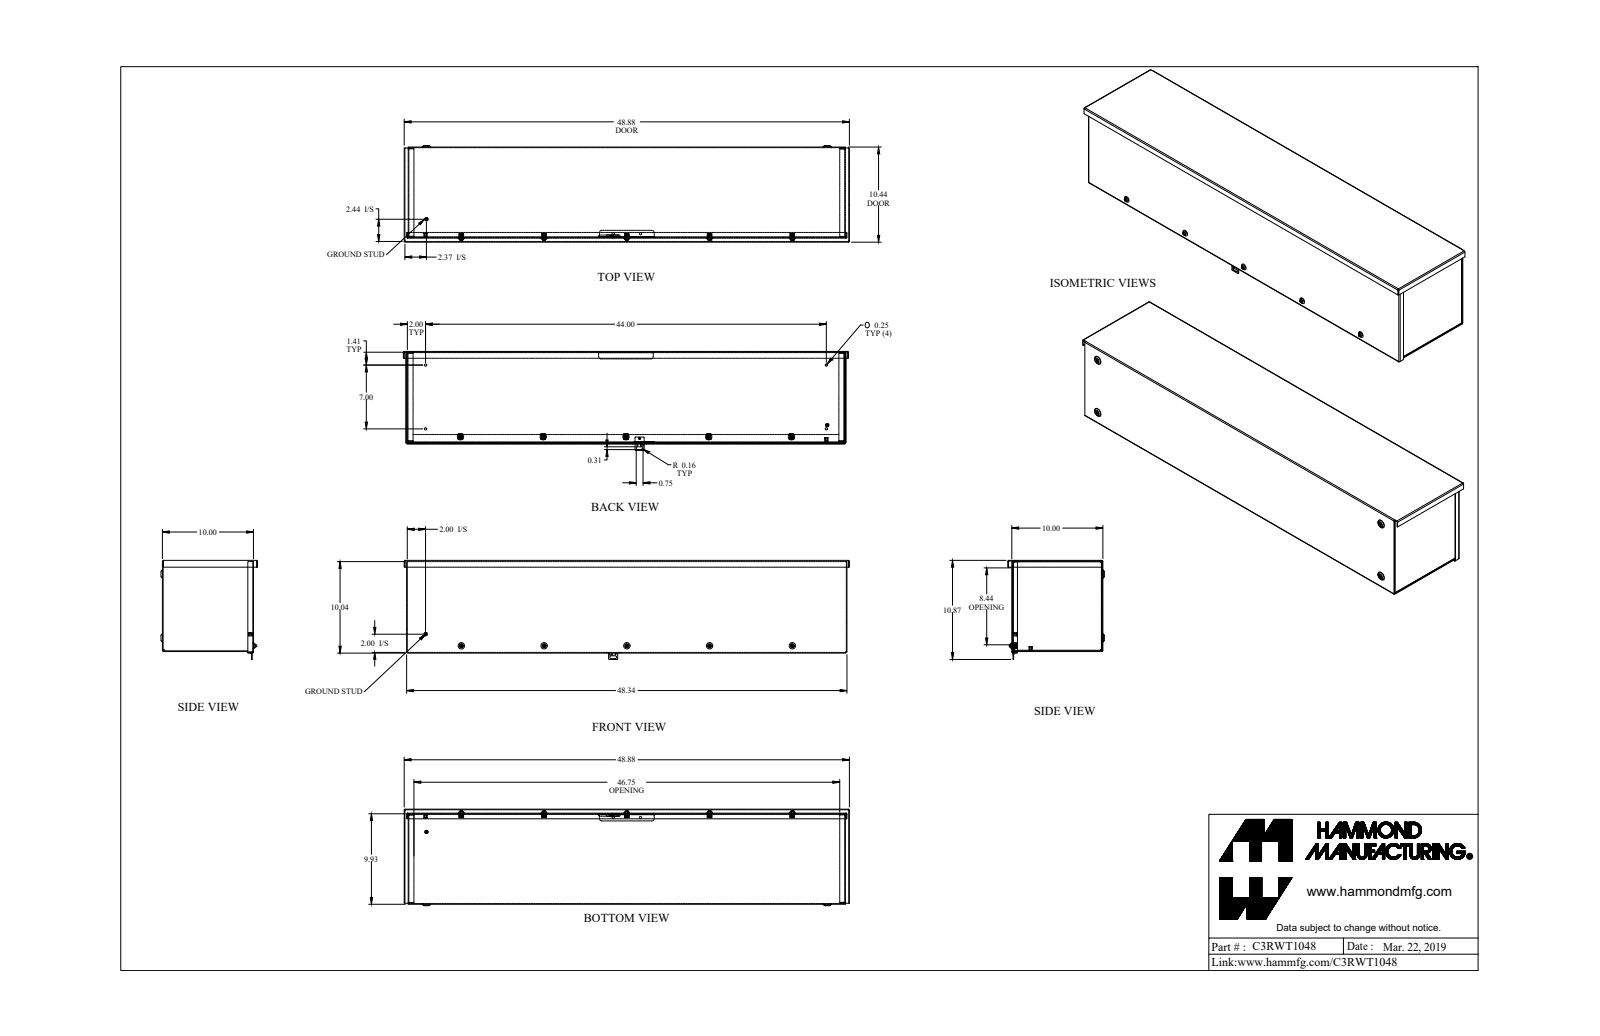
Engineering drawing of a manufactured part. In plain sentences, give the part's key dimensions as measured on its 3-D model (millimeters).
The part is named "C3RWT1048_Default". Its 3-D file was written by "SolidWorks 2019 (CONFIG_CONTROL_DESIGN)". It is 28 solids with 1006 faces: 557 planar, 313 cylindrical and 136 other. Overall it measures 1241.4 by 276.1 by 269.1 millimeters. Its volume is 2 725 000 cubic millimeters and its surface area 3 005 000 square millimeters. Round holes: 7 of diameter 4, 6 of diameter 6.4, 5 of diameter 5.4, 5 of diameter 5.8, 2 of diameter 5.2, 1 of diameter 3.2, 1 of diameter 3.5, 1 of diameter 5.1, 1 of diameter 5.5. Round bosses or shafts: 6 of diameter 4.8, 5 of diameter 3.8, 2 of diameter 9.5, 1 of diameter 12.7, 1 of diameter 9.3, 1 of diameter 5.3, 1 of diameter 3.9, 1 of diameter 3.2. Partial cylindrical surfaces (rounded edges, fillets, slot ends): 20 of radius 2, 20 of radius 2.7, 18 of radius 0.9, 18 of radius 2.7, 13 of radius 3.2, 10 of radius 0.6, 6 of radius 6.4, 5 of radius 4.3. The main face-to-face distances are 1.8, 252.2, 250.3, 254, 1217.4, 1219.2, 1215.5, 4.4, 263.3, 13. The hole center spacings are 402.8, 730.1, 99.7, 128.7, 177.8, 199.7, 222.4, 230.8.
